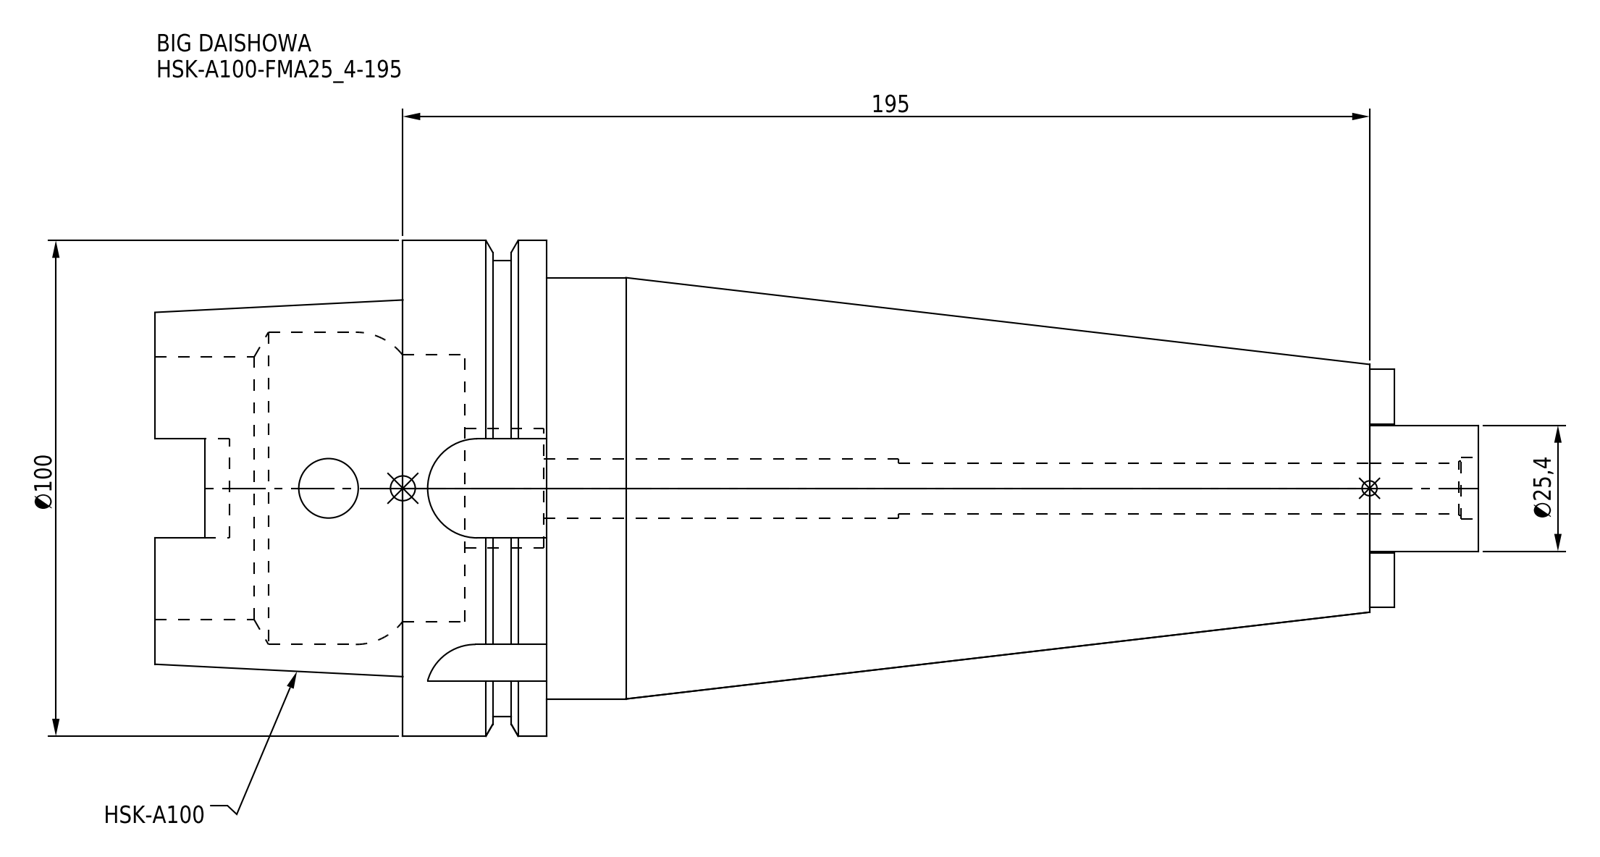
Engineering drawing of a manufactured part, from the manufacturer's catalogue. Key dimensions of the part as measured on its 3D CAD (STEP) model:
Part name (STEP PRODUCT): HSK-A100-FMA25_4-195
STEP written by: CREO PARAMETRIC BY PTC INC, 2016380 (AUTOMOTIVE_DESIGN)
Units: millimetres
Bodies: 1 solid, 106 faces (46 planar, 44 cylindrical, 16 other)
Overall size (bounding box): 267 × 100 × 100
Volume: 887 389 mm³ · Surface area: 91 072 mm²
Round holes (diameter × count): ⌀12 ×2, ⌀10.25 ×1, ⌀11 ×1, ⌀12.5 ×1, ⌀24 ×1, ⌀53 ×1, ⌀53.8 ×1, ⌀63 ×1
Round bosses / shafts (diameter × count): ⌀100 ×1, ⌀92 ×1, ⌀85 ×1, ⌀25.4 ×1
Partial cylindrical surfaces — rounded edges, fillets, slot ends (radius × count): R4.88 ×4, R10 ×4
Main face-to-face distances: 29, 16.55, 12.45, 195, 166, 182.55, 245, 79, 62.45, 50
